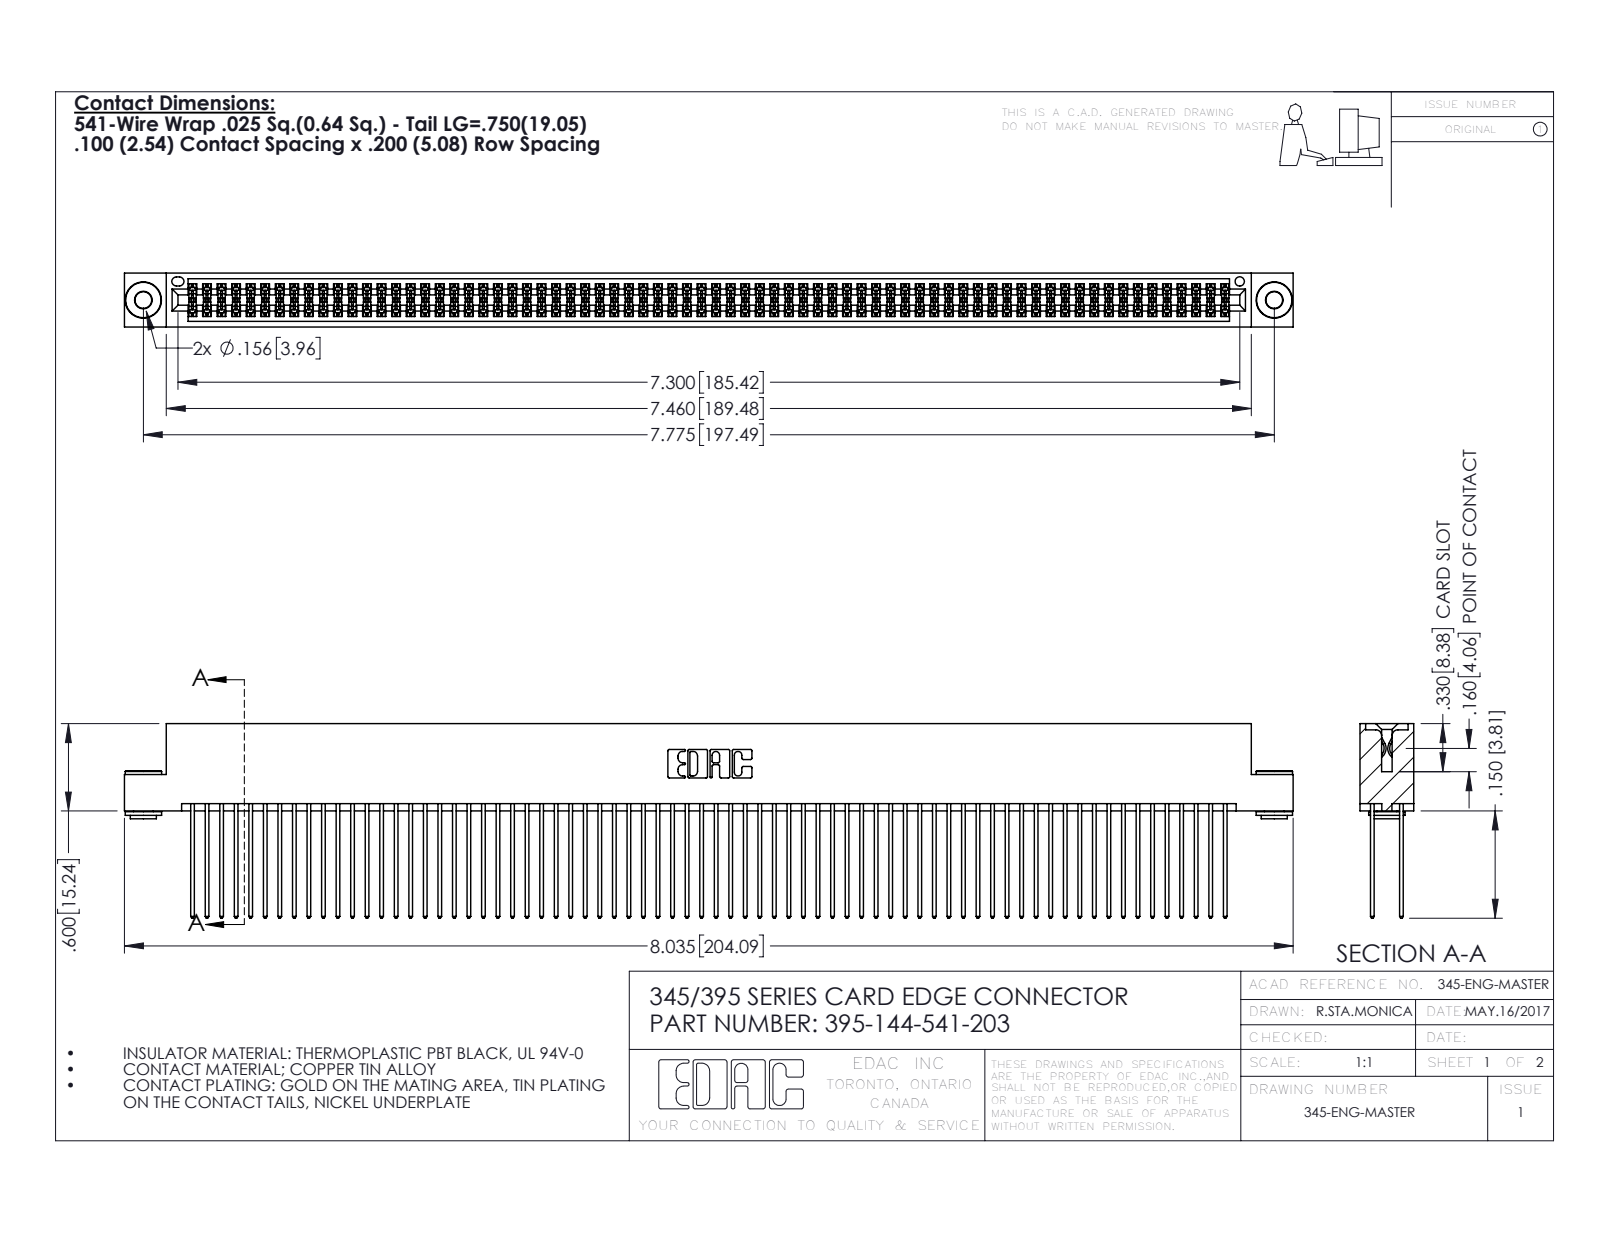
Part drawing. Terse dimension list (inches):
name: 345-292-001_345-293-141; 345 Part_Flush Mounting Lugs - 0.156 Dia-TH; 345-250-002_345-250-002-102; 395-144-541-203
written by: SolidWorks 2016 (CONFIG_CONTROL_DESIGN)
unit: in
bodies: 147 solids, 7364 faces (4842 planar, 2514 cylindrical, 8 other)
size: 8.035 × 1.337 × 0.37
volume: 1.278 in³; area: 55.24 in²
holes: 2× ⌀0.116, 2× ⌀0.156, 1× ⌀0.064
bosses: 2× ⌀0.25, 2× ⌀0.18, 2× ⌀0.136
rounds: 216× R0.006, 144× R0.01, 22× R0.01, 6× R0.007, 6× R0.031, 3× R0.026, 2× R0.014, 2× R0.019
face distances: 0.072, 0.298, 0.2, 0.025, 0.098, 0.272, 0.225, 0.37, 0.175, 0.149
hole spacings: 0.27, 7.539, 7.775
